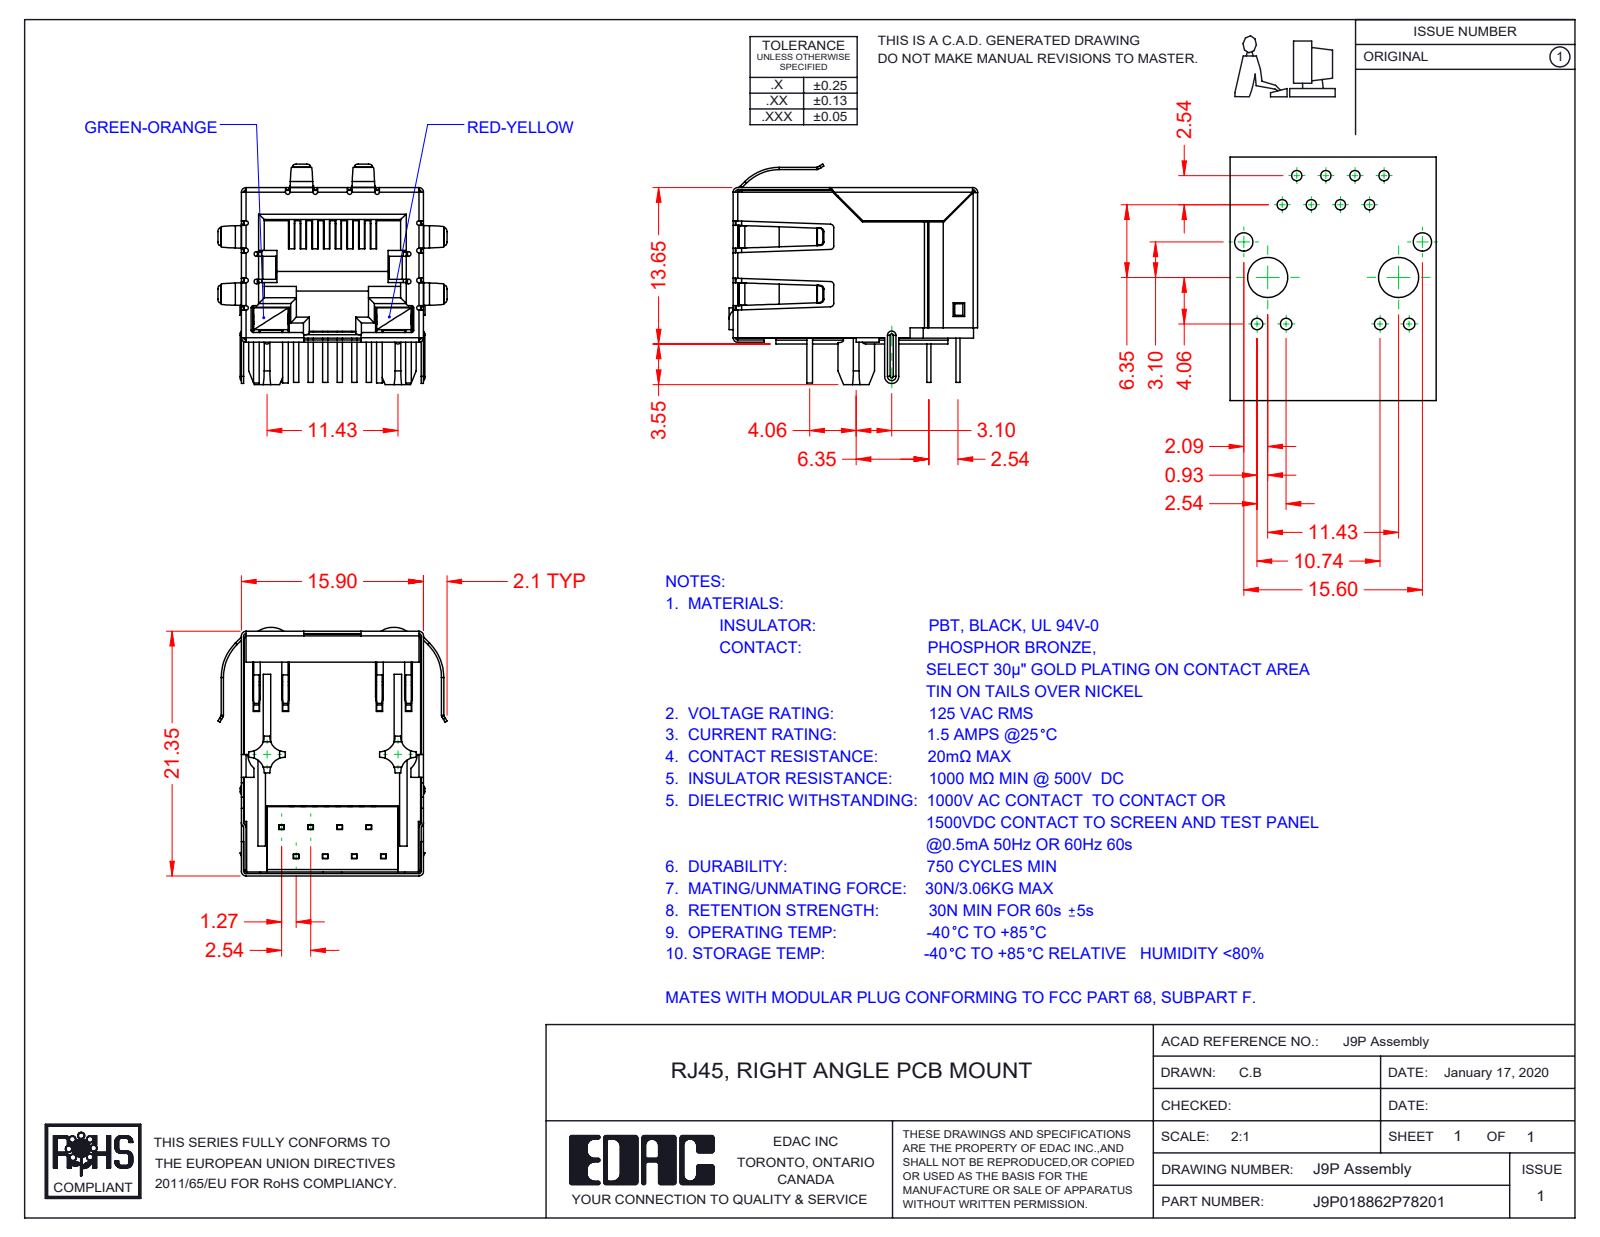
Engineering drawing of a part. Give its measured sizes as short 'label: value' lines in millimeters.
name: 9P-LED Assembly; 9P-LED Insulator; 9P-LED LED LH_7-Green-Orange; 9P-LED Contact Lock (+4 more)
written by: SolidWorks 2016 (CONFIG_CONTROL_DESIGN)
unit: mm
bodies: 13 solids, 1476 faces (1042 planar, 340 cylindrical, 94 other)
size: 21.7 × 20 × 19.25
volume: 2 687 mm³; area: 7 515 mm²
rounds: 39× R0.2, 22× R0.5, 20× R0.3, 16× R0.4, 8× R1.3, 5× R0.23, 4× R0.11, 4× R0.31
face distances: 15.45, 15.7, 15.65, 0.35, 0.54, 15.5, 12.36, 0.6, 1.4, 0.59
